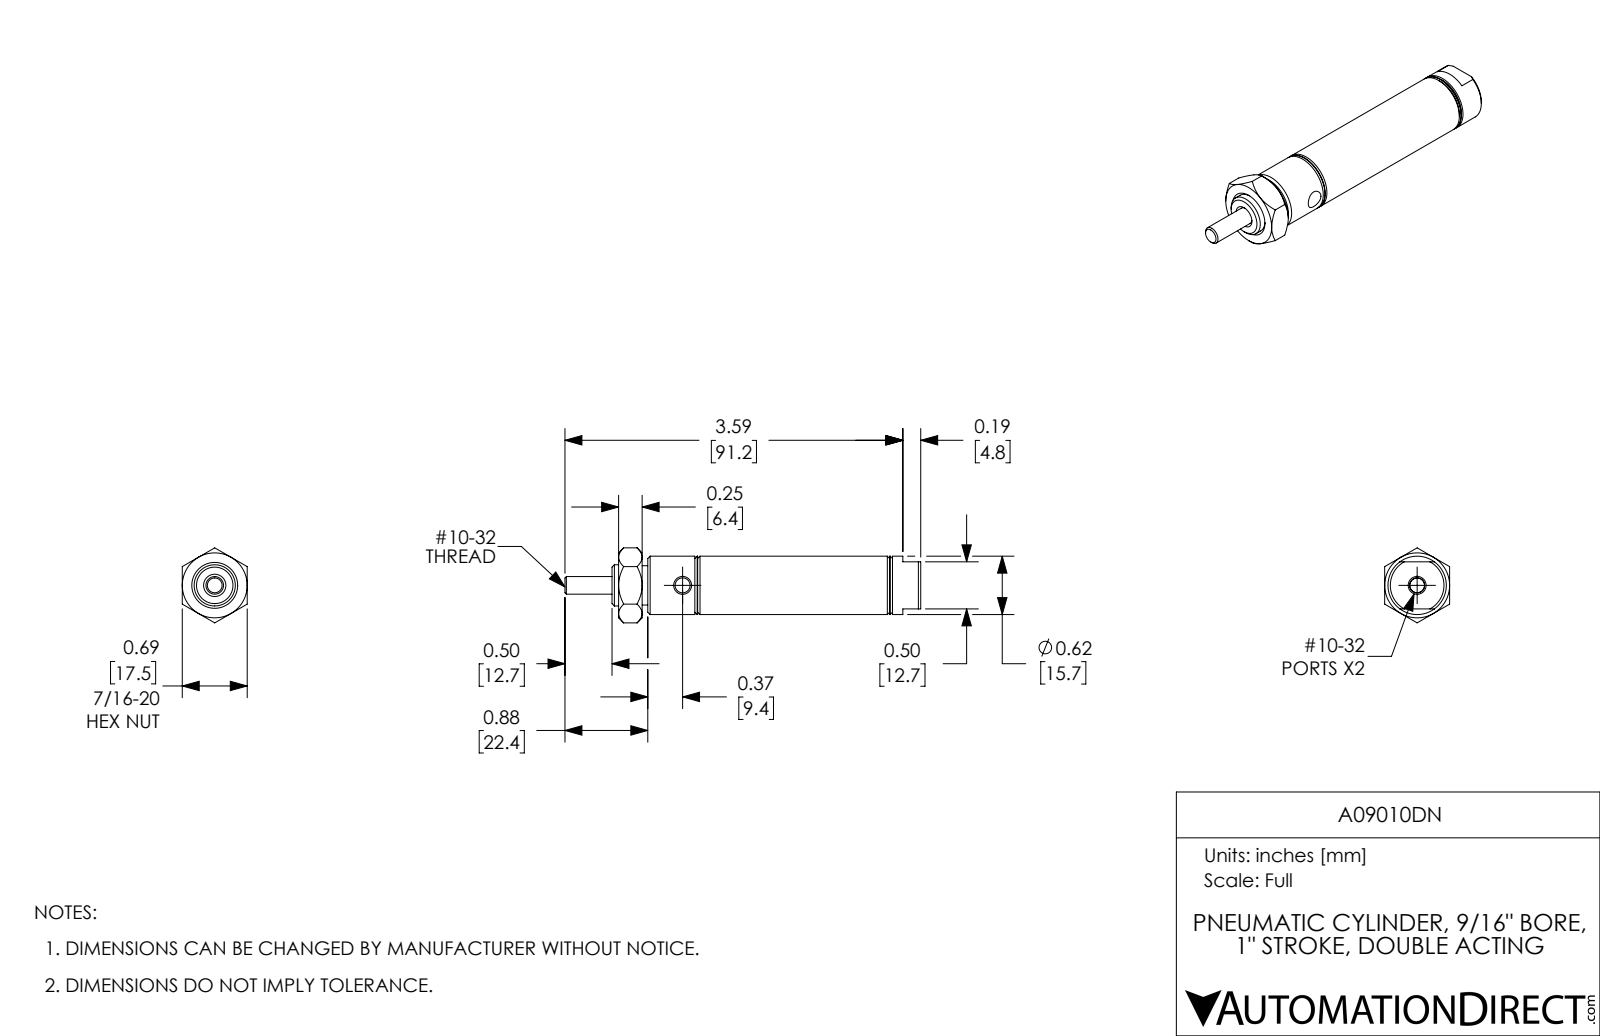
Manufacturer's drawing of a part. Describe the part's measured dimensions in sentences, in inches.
The part is named "A09010DN; A09010DN_Mounting Nut_D-154; A09010DN-Rod; A09010DN-MainBody". Its 3-D file was written by "SolidWorks 2017 (AUTOMOTIVE_DESIGN)". It is 3 solids with 100 faces: 28 planar, 34 cylindrical and 38 other. Overall it measures 3.78 by 0.797 by 0.69 inches. Its volume is 0.757 cubic inches and its surface area 15.33 square inches. Round holes: 2 of diameter 0.159, 2 of diameter 0.19, 1 of diameter 0.156, 1 of diameter 0.187, 1 of diameter 0.437, 1 of diameter 0.563. Round bosses or shafts: 1 of diameter 0.62, 1 of diameter 0.417. The main face-to-face distances are 0.7, 2.2, 0.5, 0.69, 1.2, 1.5, 2.96, 2.26, 0.76, 1.
